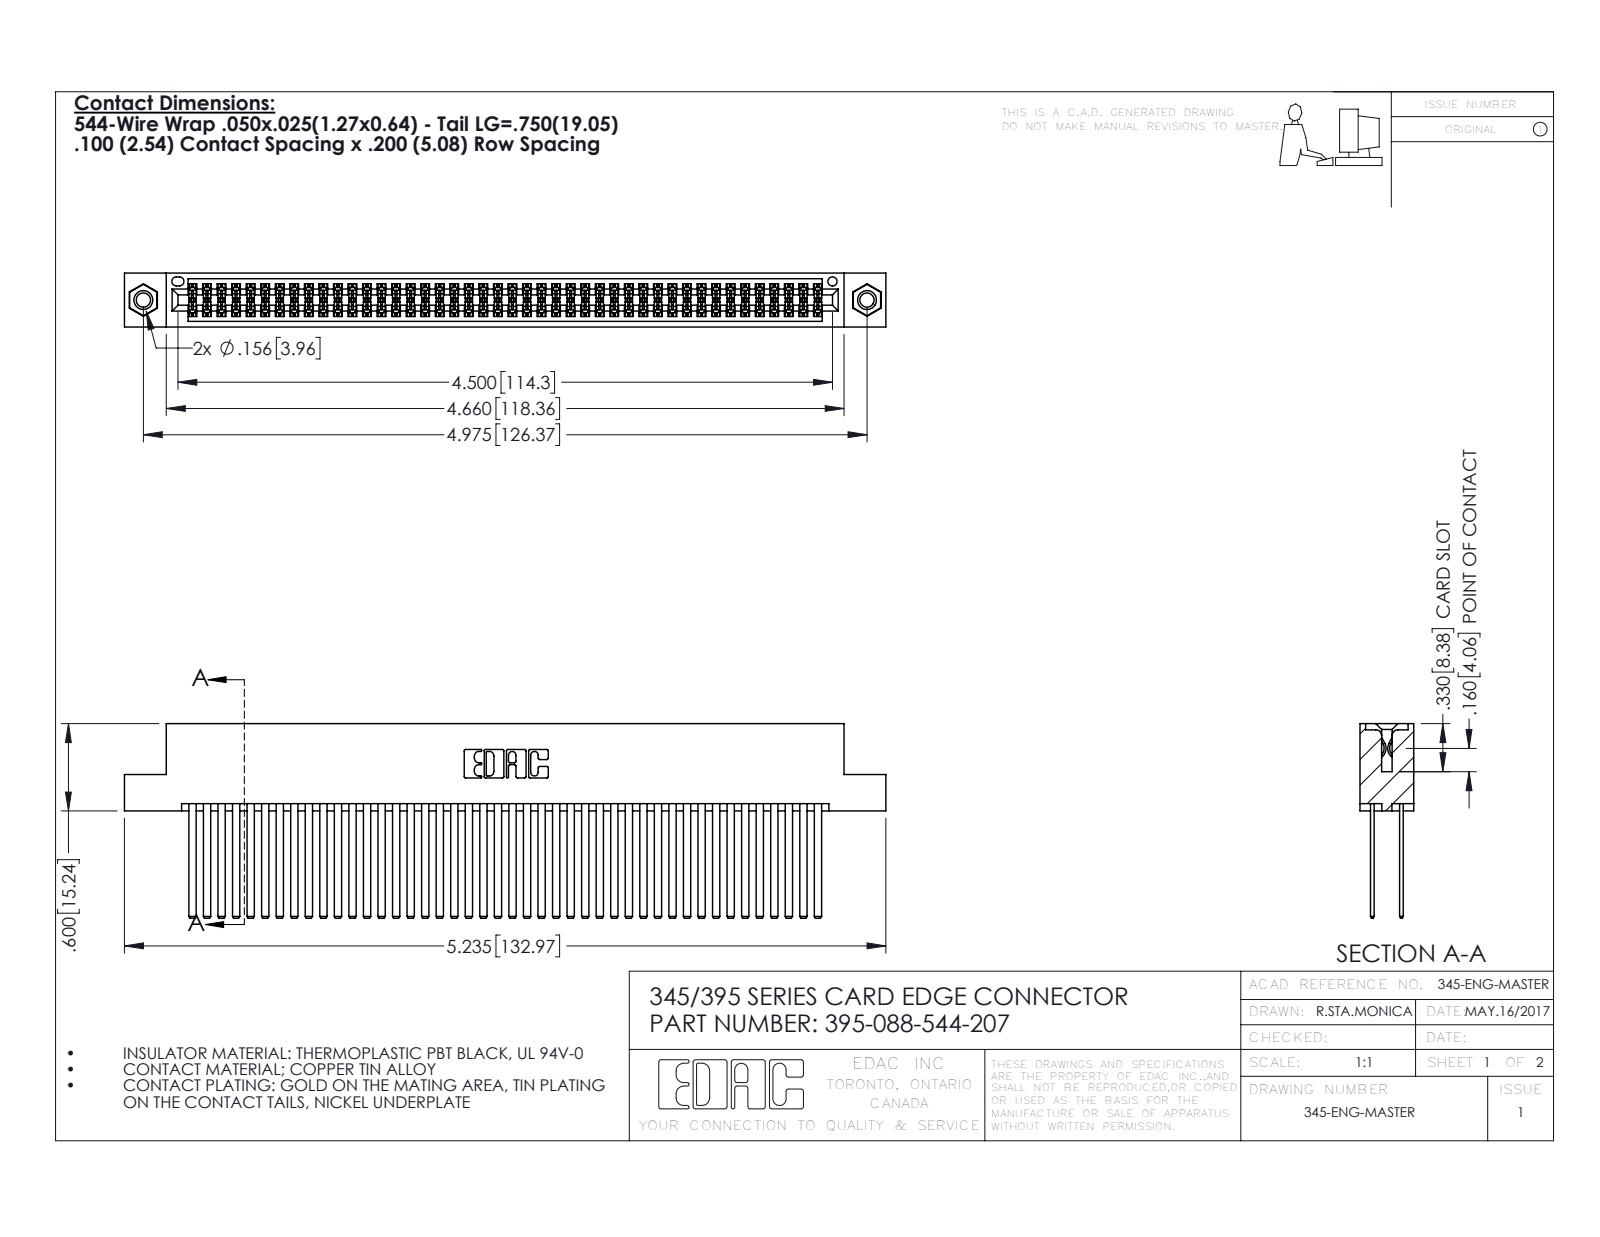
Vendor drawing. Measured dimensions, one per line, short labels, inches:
name: 395-088-544-207; 345-292-001_345-293-144; 345 Part_Flush Mounting Lugs - 0.156 Dia-TI; 345-250-001_345-250-005-103
written by: SolidWorks 2016 (CONFIG_CONTROL_DESIGN)
unit: in
bodies: 91 solids, 4058 faces (2664 planar, 1378 cylindrical, 16 other)
size: 5.235 × 1.337 × 0.37
volume: 0.864 in³; area: 38.14 in²
holes: 2× ⌀0.098, 2× ⌀0.125, 2× ⌀0.156, 1× ⌀0.064
bosses: 2× ⌀0.155
rounds: 132× R0.006, 22× R0.01, 6× R0.007, 6× R0.031, 3× R0.026, 2× R0.014, 2× R0.019, 2× R0.022
face distances: 0.2, 0.025, 0.072, 0.098, 0.272, 0.298, 0.225, 0.175, 0.37, 0.05
hole spacings: 0.27, 4.739, 4.975
